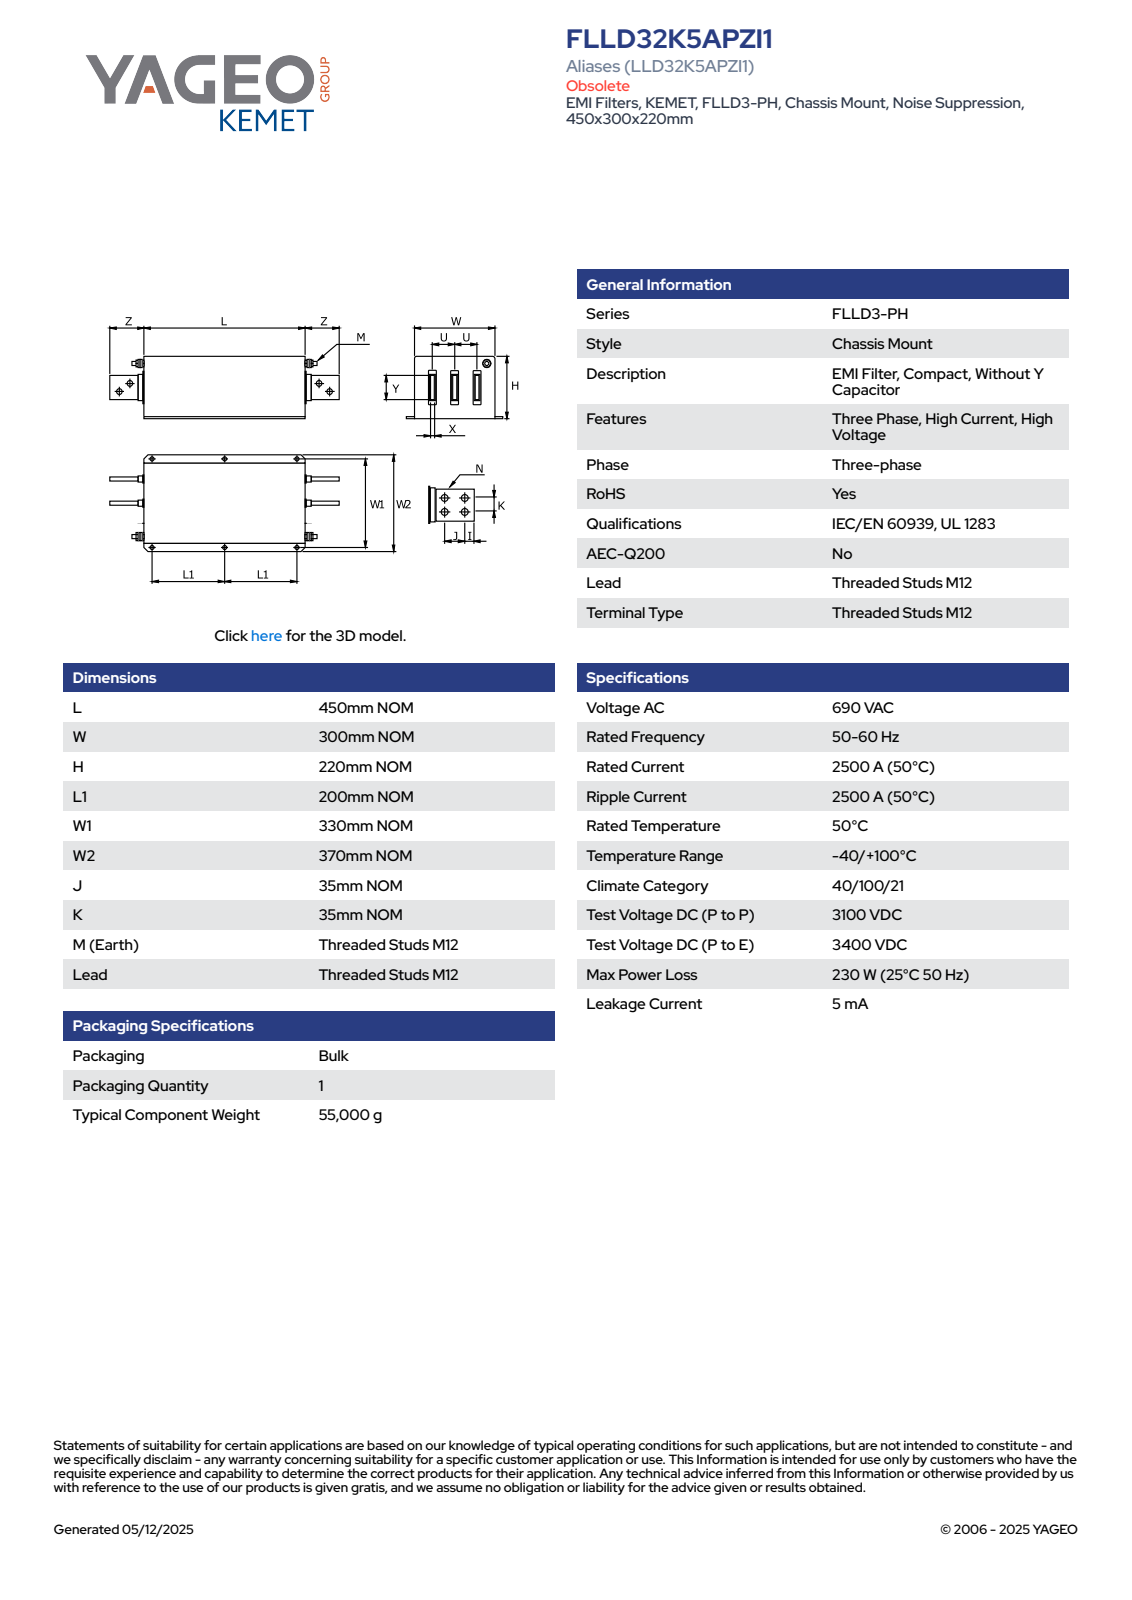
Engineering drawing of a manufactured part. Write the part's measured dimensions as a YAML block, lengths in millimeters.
part_name: "Busbar 15x80^FLLD32K5APVI1_EXT; Rivet Ø3.2x4; 091-00227 Busbar insulation 15x80 RevD_Busbar config; HEX BOLT M12x45_91280A722 (+8 more)"
step_written_by: "SolidWorks 2021 (AUTOMOTIVE_DESIGN)"
units: millimeters
bodies: {solids: 84, faces: 3072, planar: 692, cylindrical: 970, other: 1410}
overall_size: [670, 370, 220]
volume: 1994000
surface_area: 1586000
round_holes:
  - {diameter: 1.8, count: 20}
  - {diameter: 3.4, count: 14}
  - {diameter: 3.2, count: 10}
  - {diameter: 14, count: 9}
  - {diameter: 12, count: 6}
  - {diameter: 5, count: 4}
  - {diameter: 5.2, count: 4}
  - {diameter: 13, count: 1}
round_bosses_or_shafts:
  - {diameter: 3.2, count: 14}
  - {diameter: 7, count: 4}
  - {diameter: 24, count: 1}
  - {diameter: 12, count: 1}
partial_cylinders:
  - {radius: 2, count: 60}
  - {radius: 0.5, count: 52}
  - {radius: 0.2, count: 36}
  - {radius: 0.25, count: 24}
  - {radius: 1, count: 18}
  - {radius: 2.5, count: 10}
  - {radius: 1.5, count: 4}
  - {radius: 3, count: 2}
face_to_face_distances: [2, 1, 298, 448, 218, 220, 217, 219, 446, 296]
hole_center_spacings: [35, 49.5, 93.75, 100, 148.66, 165.37, 195, 263.93]
